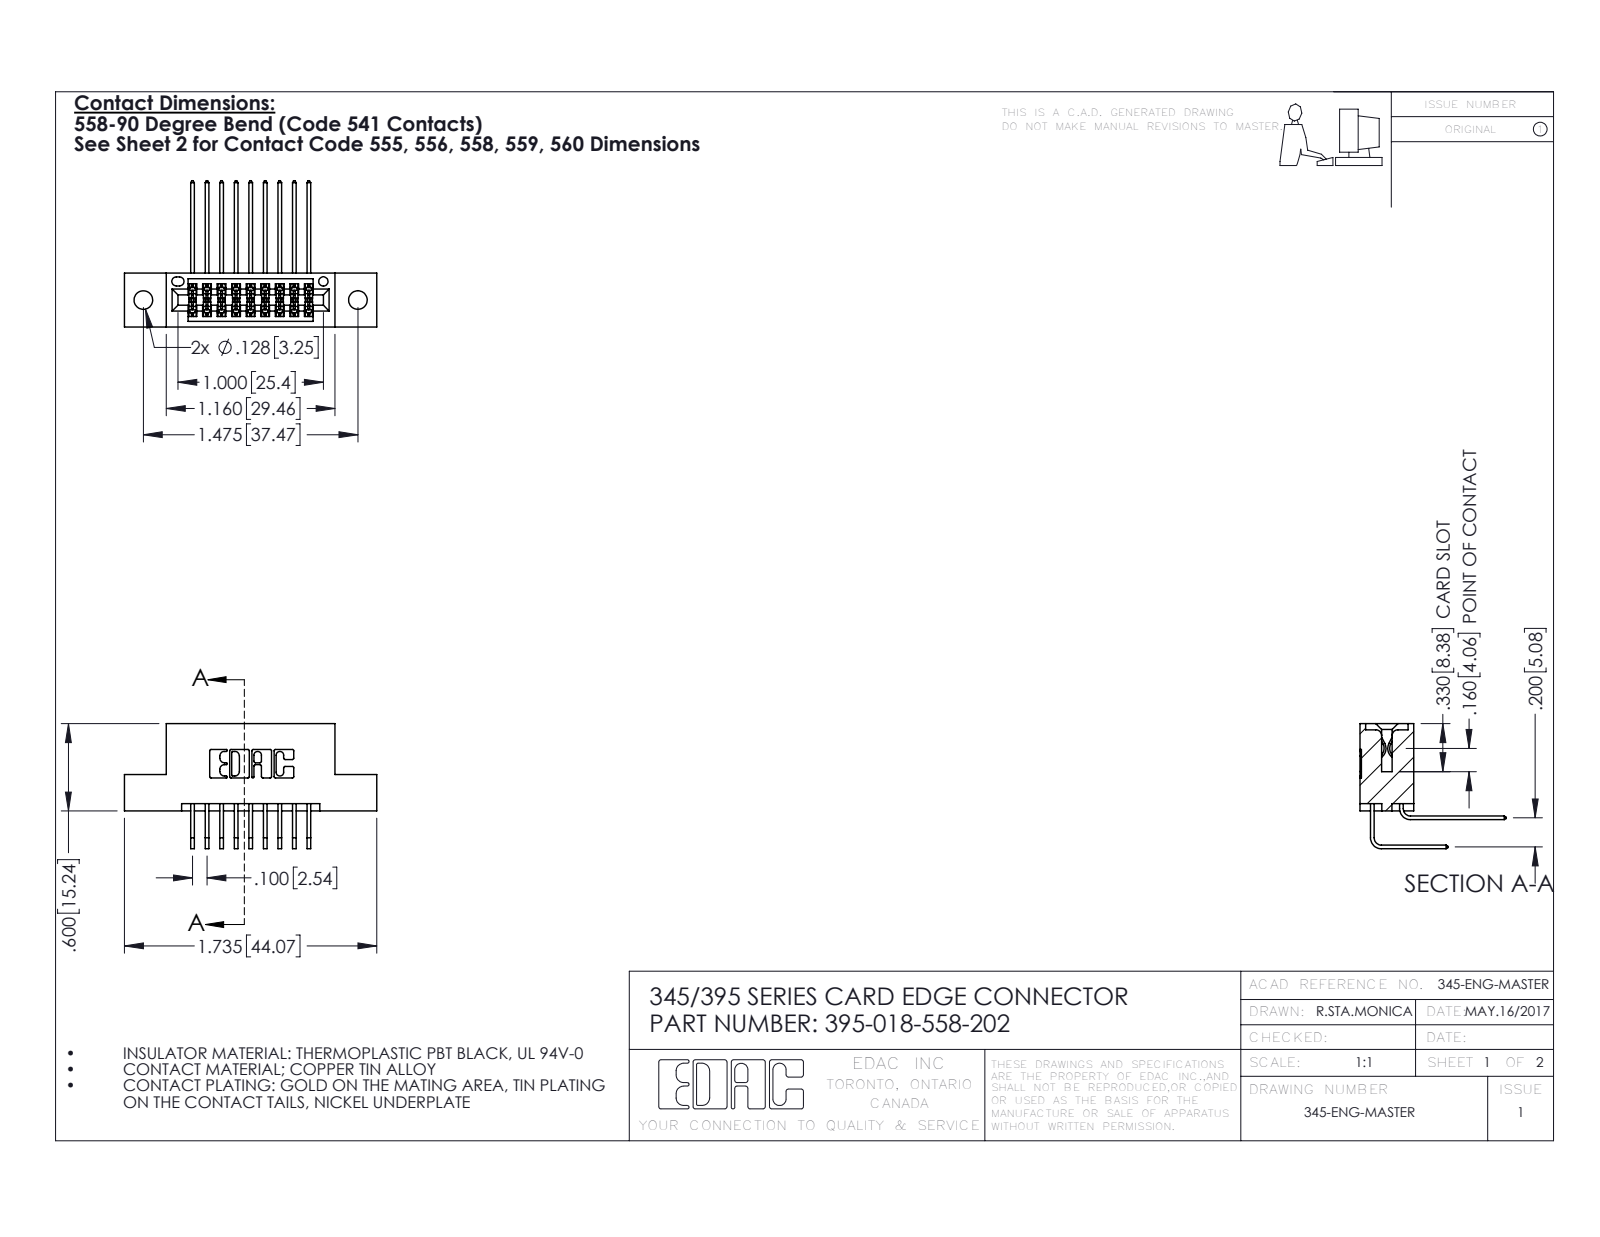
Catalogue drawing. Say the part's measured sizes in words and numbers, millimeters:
The part is named "345-292-001_558 559 Tail - 1; 345 Part_Flush Mounting Lugs - 0.128 Dia; 345-292-001_558 Tail - 2; 395-018-558-202". Its 3-D file was written by "SolidWorks 2016 (CONFIG_CONTROL_DESIGN)". It is 19 solids with 1062 faces: 710 planar, 352 cylindrical and 0 other. Overall it measures 44.1 by 25.5 by 21.8 millimeters. Its volume is 4 050 cubic millimeters and its surface area 5 551 square millimeters. Round holes: 2 of diameter 3.3, 1 of diameter 1.6. Partial cylindrical surfaces (rounded edges, fillets, slot ends): 28 of radius 0.2, 22 of radius 0.3, 6 of radius 0.2, 6 of radius 0.8, 3 of radius 0.7, 2 of radius 0.4, 2 of radius 0.5, 2 of radius 0.6. The main face-to-face distances are 5.1, 1.8, 7.6, 9.4, 2.5, 2.5, 6.9, 0.6, 15.2, 5.7. The hole center spacings are 6.9, 31.6, 37.5.
